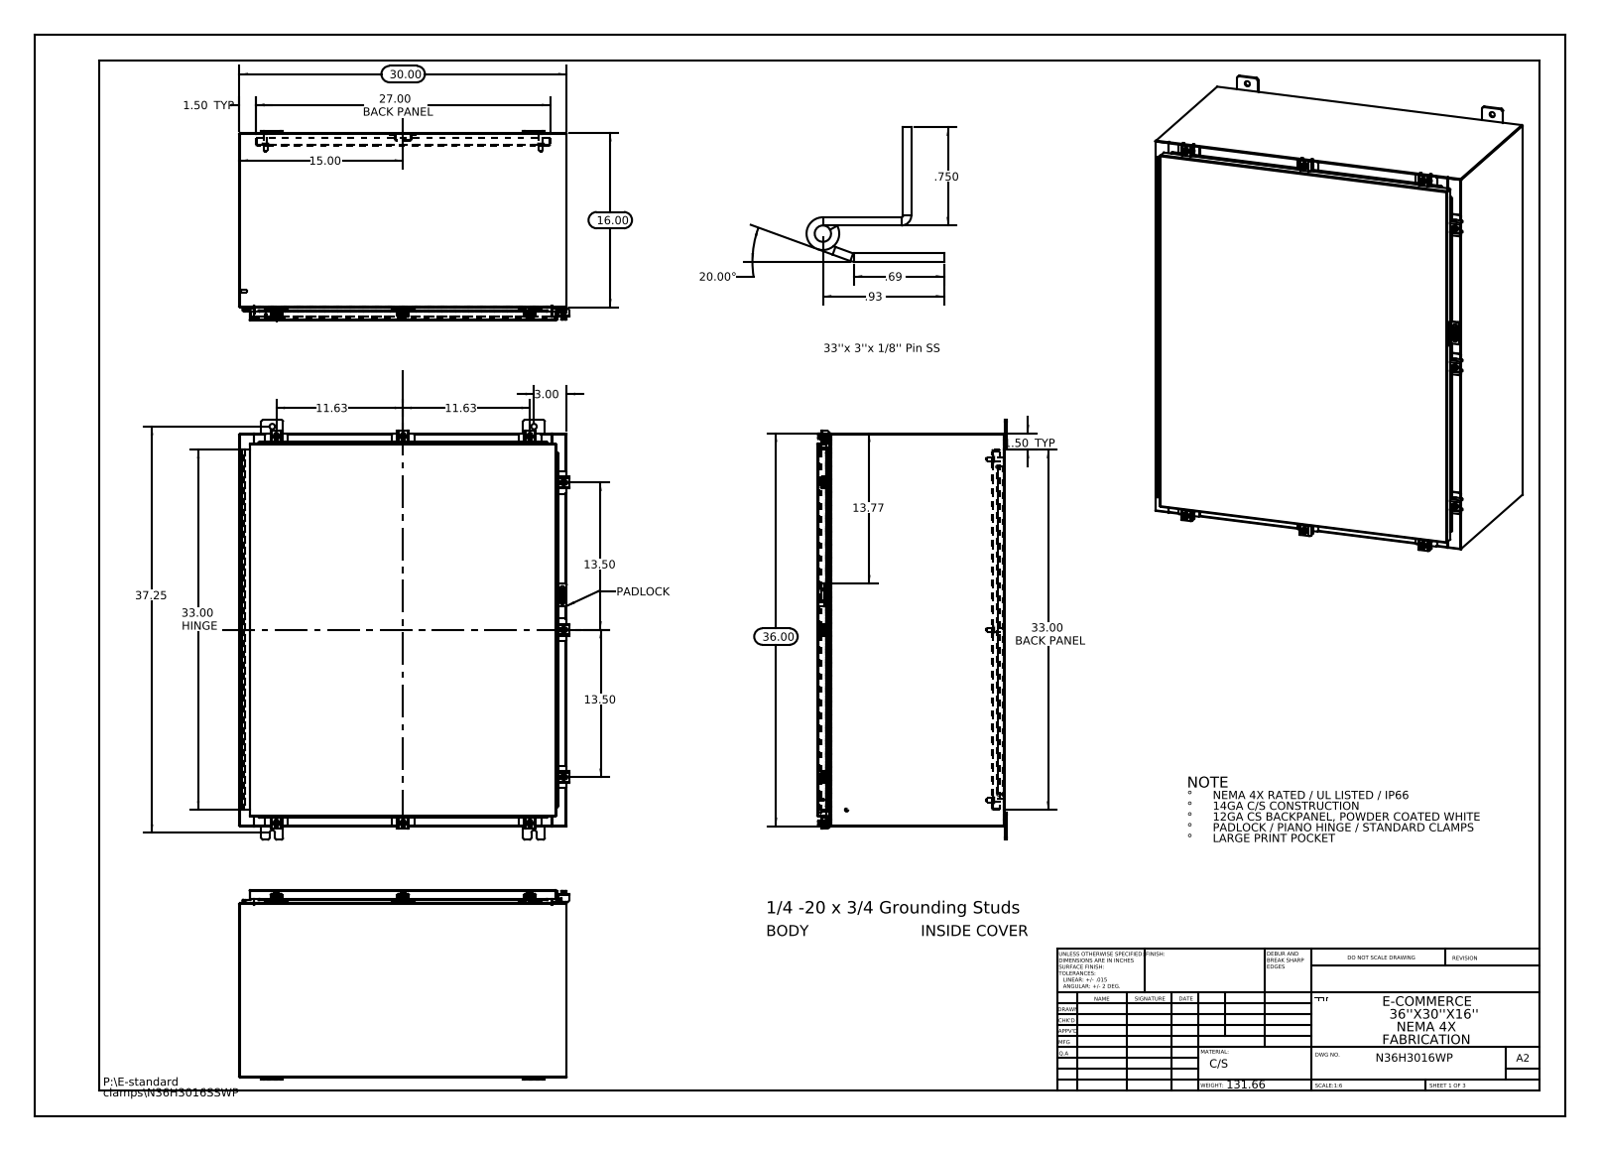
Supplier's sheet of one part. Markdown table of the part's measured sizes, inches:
| quantity | value |
| --- | --- |
| part name | N36H3016SSWP Cover; N36H3016SSWP Hinge Cover Side; N36H3016SSWP Standard Clamps; N36H3016SSWP Hinge Enclosure Side2 (+8 more) |
| STEP written by | SolidWorks 2013 (CONFIG_CONTROL_DESIGN) |
| units | inches |
| bodies | 67 solids, 2482 faces (1294 planar, 1036 cylindrical, 152 other) |
| overall size | 38.5 × 30.211 × 17.389 |
| volume | 461 in³ |
| surface area | 11 627 in² |
| round holes (diameter × count) | 0.5 × 10, 0.213 × 9, 0.26 × 9, 0.125 × 2 |
| round bosses / shafts (diameter × count) | 0.25 × 10, 0.5 × 9, 0.399 × 9, 0.625 × 6, 0.375 × 6, 0.33 × 6, 0.315 × 2, 0.236 × 2 |
| partial cylindrical surfaces (radius × count) | 0.06 × 42, 0.013 × 31, 0.088 × 25, 0.19 × 24, 0.12 × 18, 0.141 × 18, 0.05 × 13, 0.08 × 12 |
| main face-to-face distances | 0.075, 17.126, 29.925, 17.051, 17.201, 0.104, 35.925, 16.126, 1, 1.075 |
| hole center spacings | 15.625, 17.754, 29.694, 33.366, 37.309, 25.25, 35.451, 1.858 |
